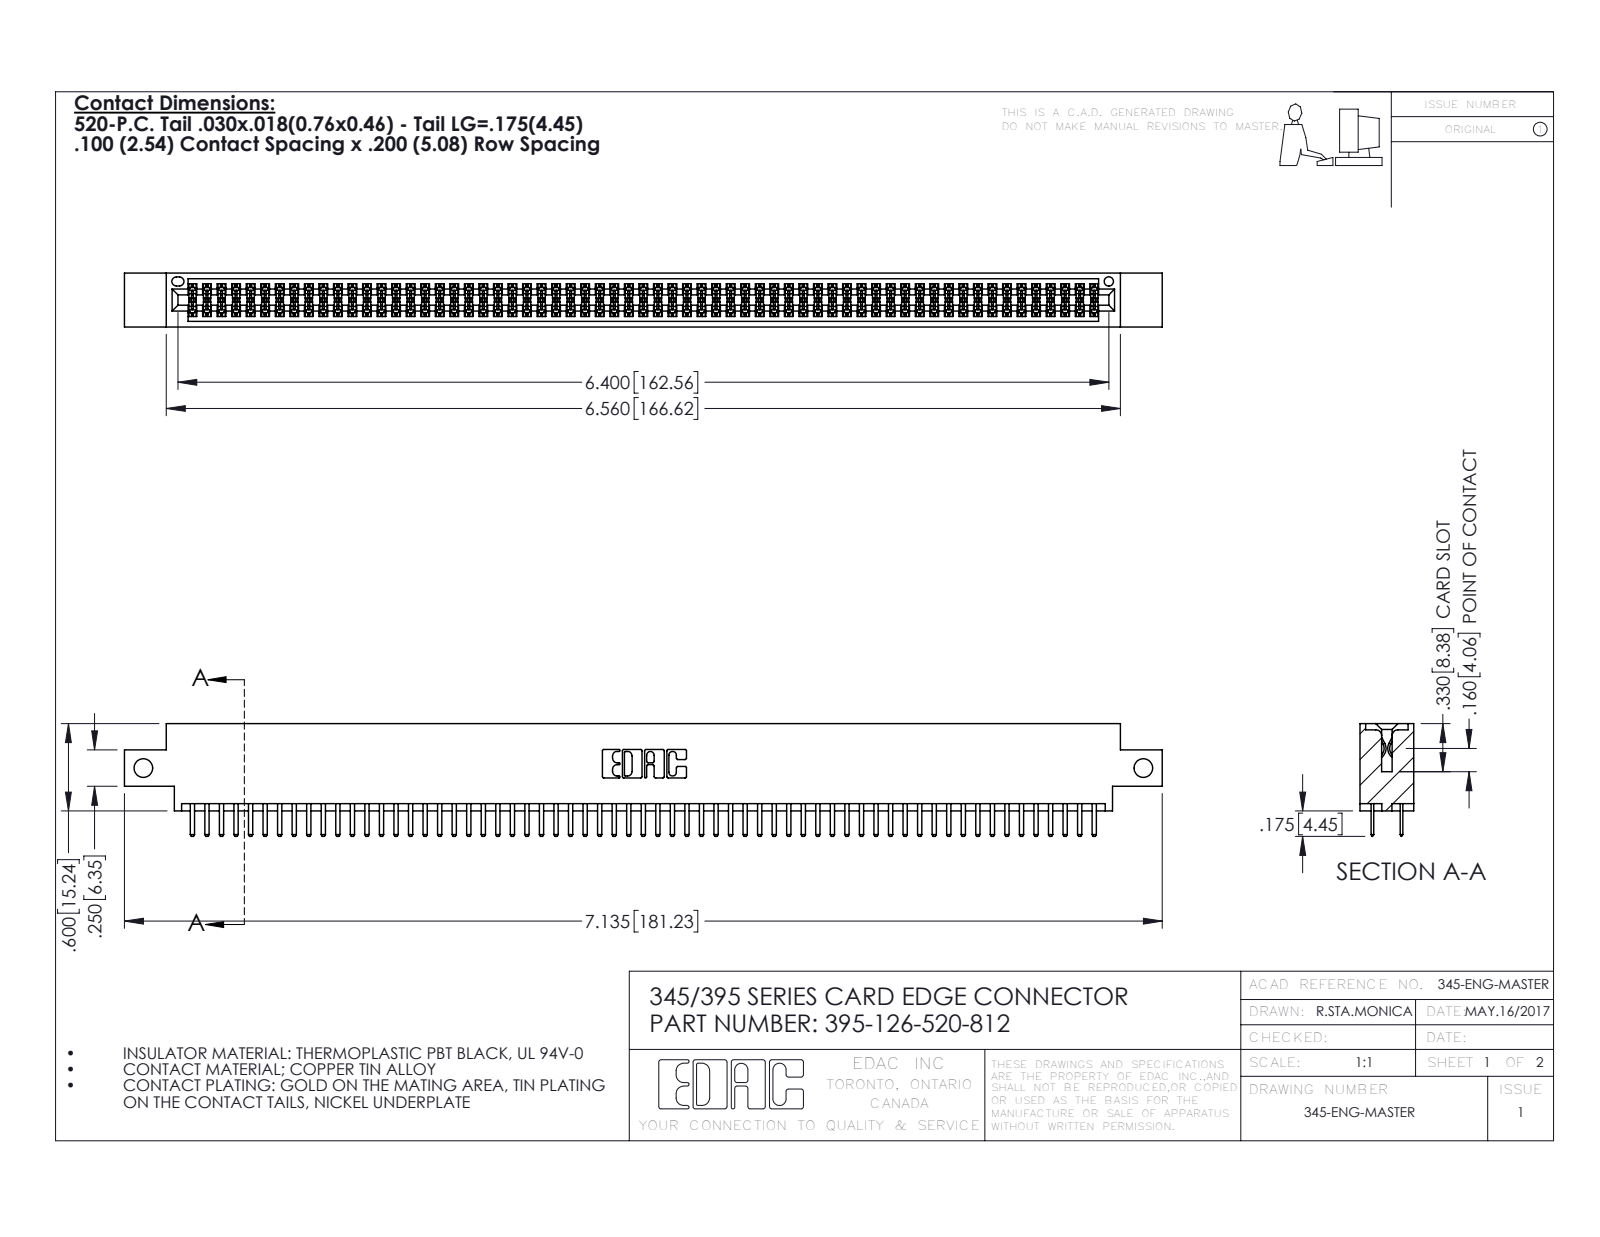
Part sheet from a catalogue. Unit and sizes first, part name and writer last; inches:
Units: inches
Overall size (bounding box): 7.135 × 0.775 × 0.37
Round holes (diameter × count): ⌀0.128 ×2, ⌀0.064 ×1
Partial cylindrical surfaces — rounded edges, fillets, slot ends (radius × count): R0.006 ×189, R0.01 ×130, R0.01 ×22, R0.007 ×6, R0.031 ×6, R0.026 ×3, R0.014 ×2, R0.019 ×2
Main face-to-face distances: 0.072, 0.298, 0.2, 0.37, 0.098, 0.272, 0.025, 0.225, 0.022, 0.072
Hole centre spacings: 6.875
Volume: 1.071 in³ · Surface area: 40.66 in²
Bodies: 127 solids, 6934 faces (4494 planar, 2440 cylindrical, 0 other)
Part name (STEP PRODUCT): 345-292-001_345-293-120; 345 Part_0.170 Offset - Side Mount; 395-126-520-812
STEP written by: SolidWorks 2016 (CONFIG_CONTROL_DESIGN)
